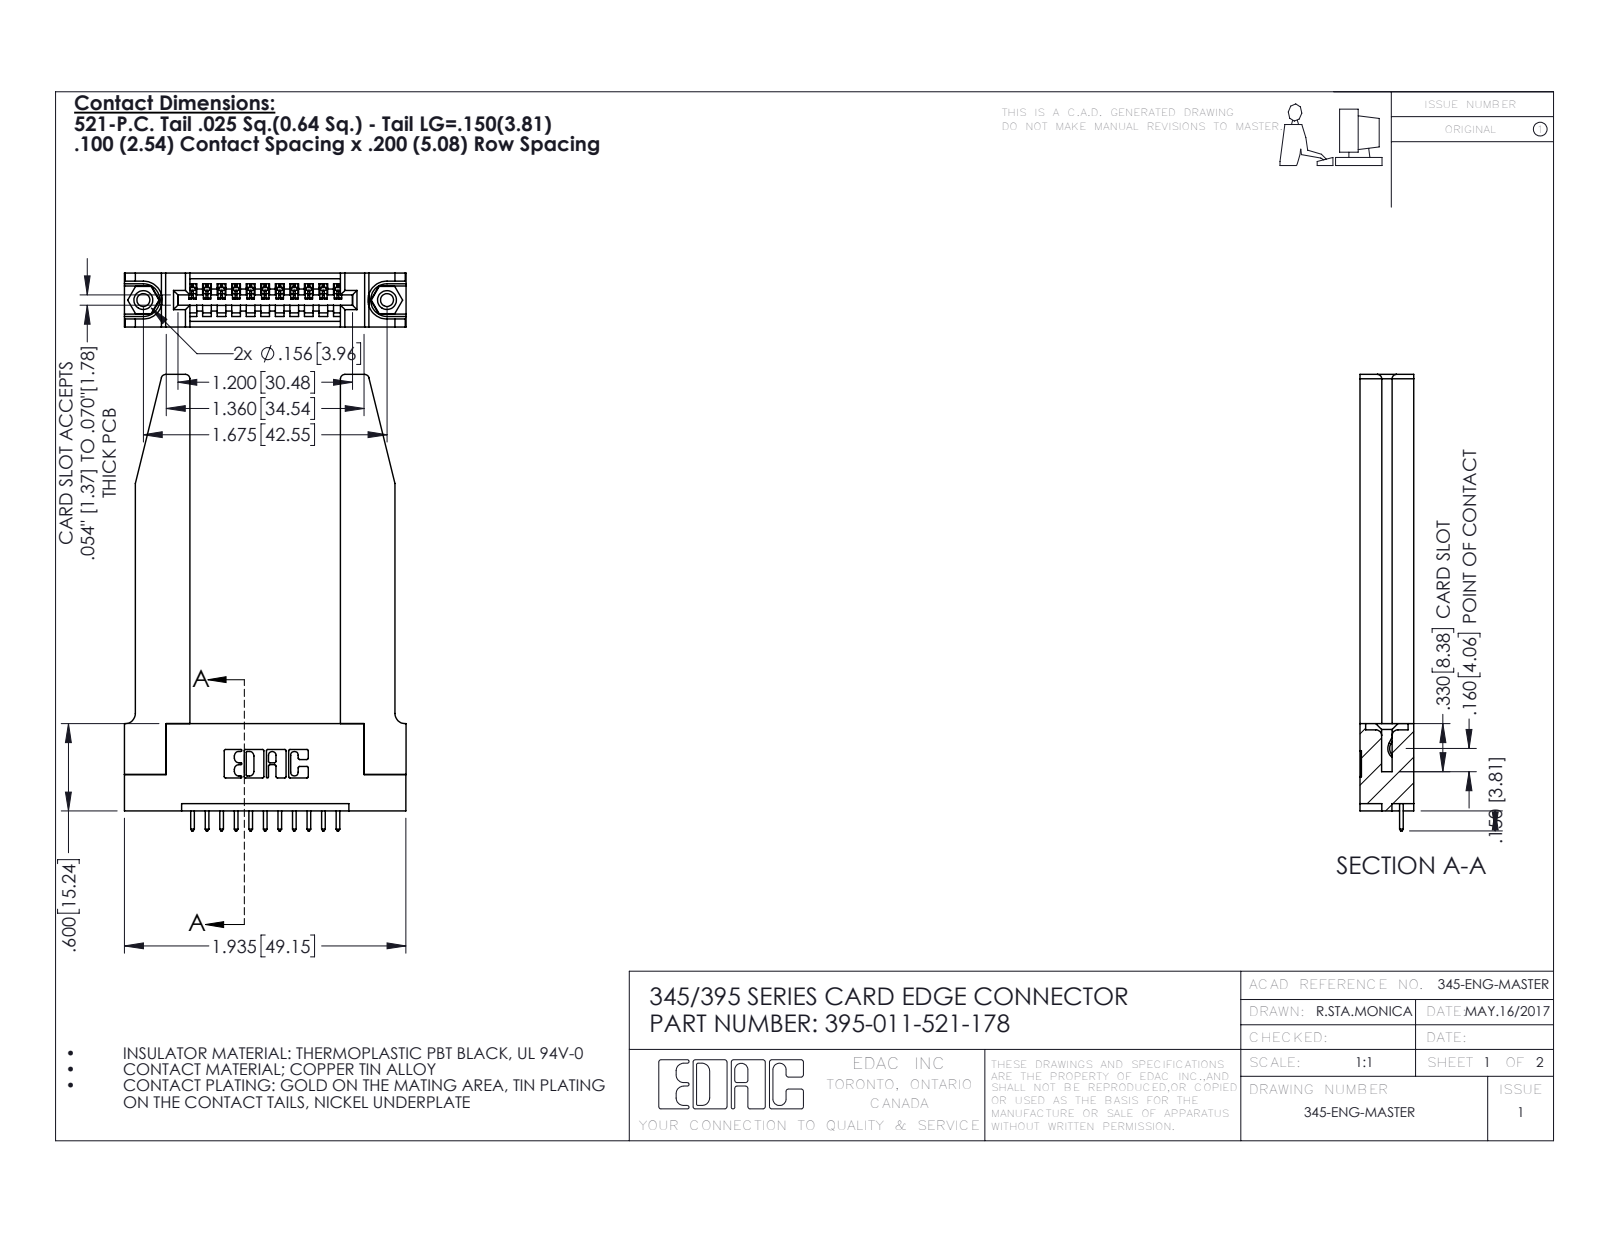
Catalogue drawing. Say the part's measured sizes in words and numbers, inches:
The part is named "395-011-521-178; 345-292-001_345-293-121; 345-220-078_345-220-078; 345-250-001_345-250-001-102 (+1 more)". Its 3-D file was written by "SolidWorks 2016 (CONFIG_CONTROL_DESIGN)". It is 16 solids with 998 faces: 662 planar, 284 cylindrical and 52 other. Overall it measures 3.137 by 1.936 by 0.37 inches. Its volume is 0.742 cubic inches and its surface area 18.8 square inches. Round holes: 2 of diameter 0.089, 2 of diameter 0.125, 2 of diameter 0.156, 1 of diameter 0.064. Round bosses or shafts: 2 of diameter 0.155. Partial cylindrical surfaces (rounded edges, fillets, slot ends): 22 of radius 0.006, 22 of radius 0.01, 22 of radius 0.01, 8 of radius 0.03, 6 of radius 0.007, 6 of radius 0.031, 3 of radius 0.026, 2 of radius 0.031. The main face-to-face distances are 0.37, 0.072, 0.298, 0.148, 0.15, 0.2, 0.077, 0.22, 1.035, 0.098. The hole center spacings are 0.27, 1.443, 1.675.
